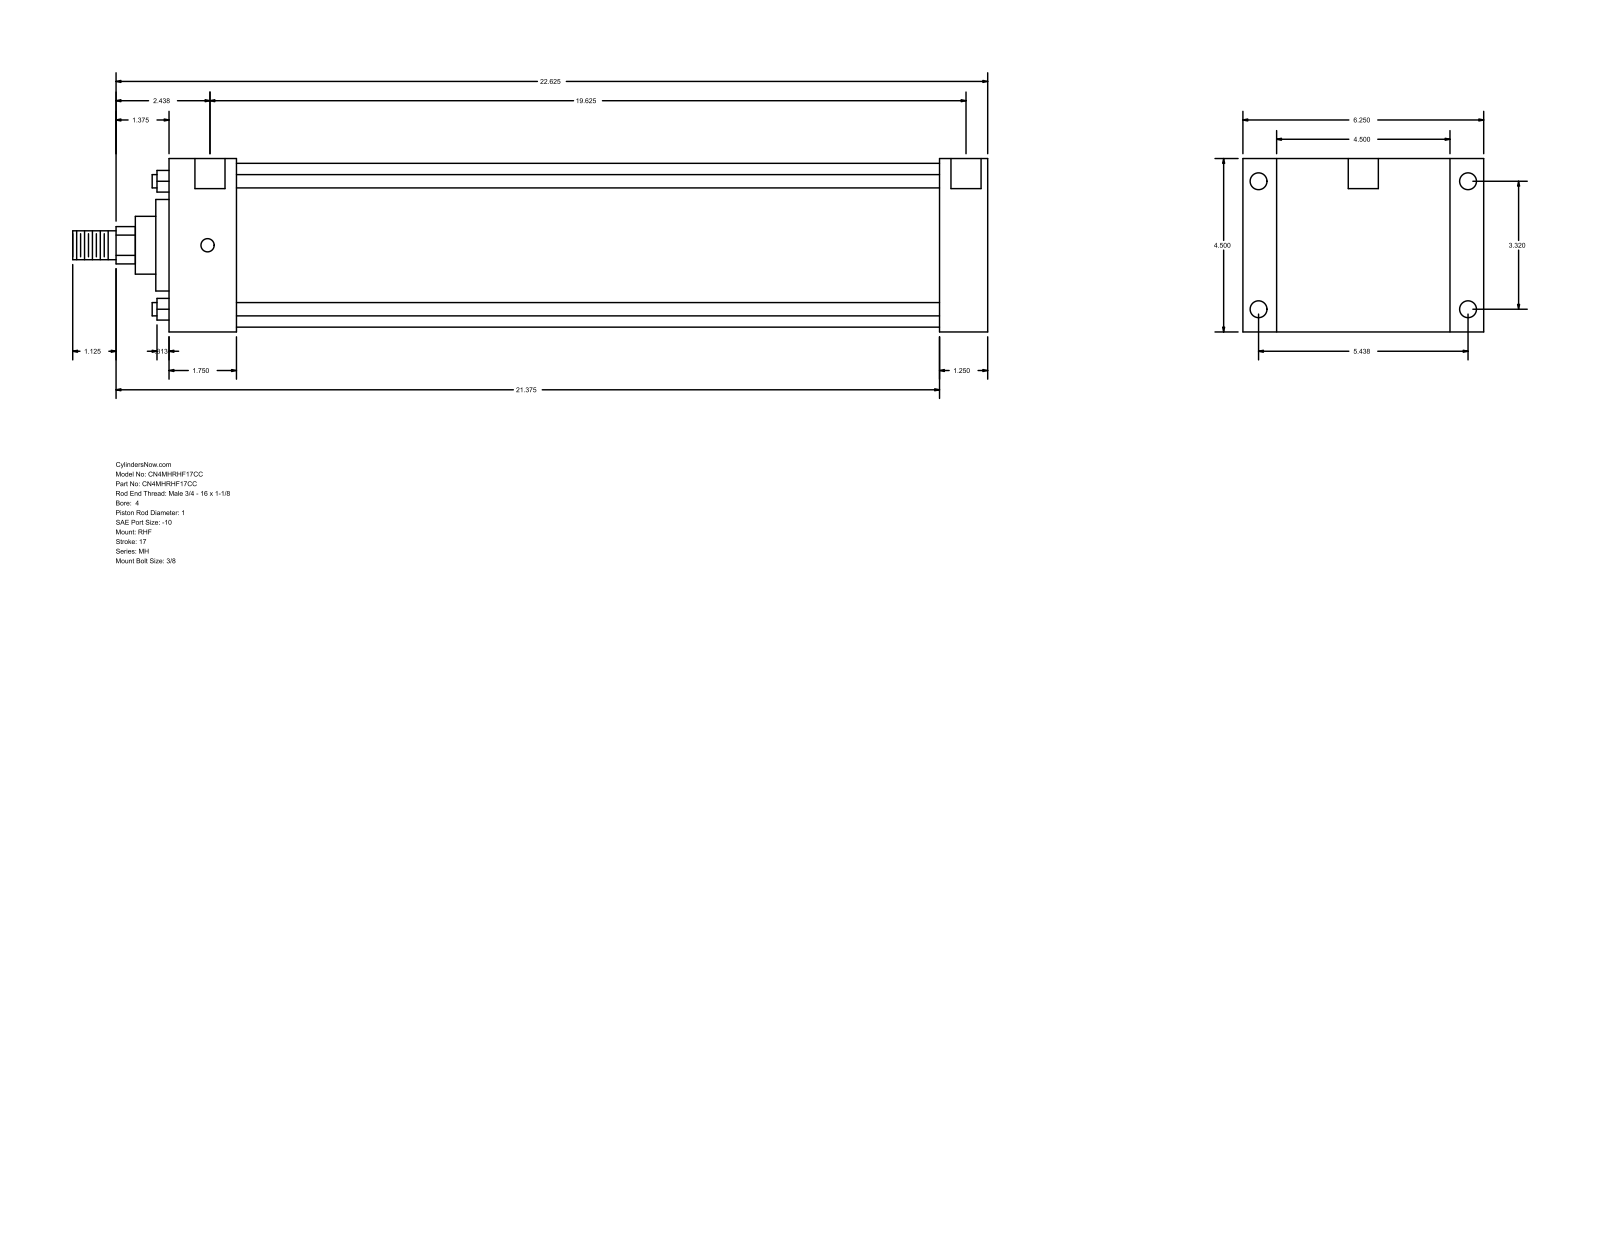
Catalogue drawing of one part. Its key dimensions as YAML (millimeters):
part_name: "MH_RHF__0400_1"
step_written_by: "GSSL Pune (CONFIG_CONTROL_DESIGN)"
units: millimeters
bodies: {solids: 0, faces: 90, planar: 61, cylindrical: 29, other: 0}
overall_size: [603.25, 158.75, 114.3]
round_holes:
  - {diameter: 8.73, count: 4}
  - {diameter: 11.13, count: 4}
  - {diameter: 19.84, count: 2}
round_bosses_or_shafts:
  - {diameter: 8.76, count: 4}
  - {diameter: 107.95, count: 1}
  - {diameter: 60.33, count: 1}
  - {diameter: 38.1, count: 1}
  - {diameter: 25.4, count: 1}
  - {diameter: 19.05, count: 1}
partial_cylinders:
  - {radius: 12.29, count: 1}
face_to_face_distances: [114.3, 539.75, 508, 31.75, 22.23, 136.53, 44.46, 463.54, 495.29, 158.76]
hole_center_spacings: [84.32, 138.12, 161.82, 501.65, 1.58, 1.59, 498.48, 500.06]
